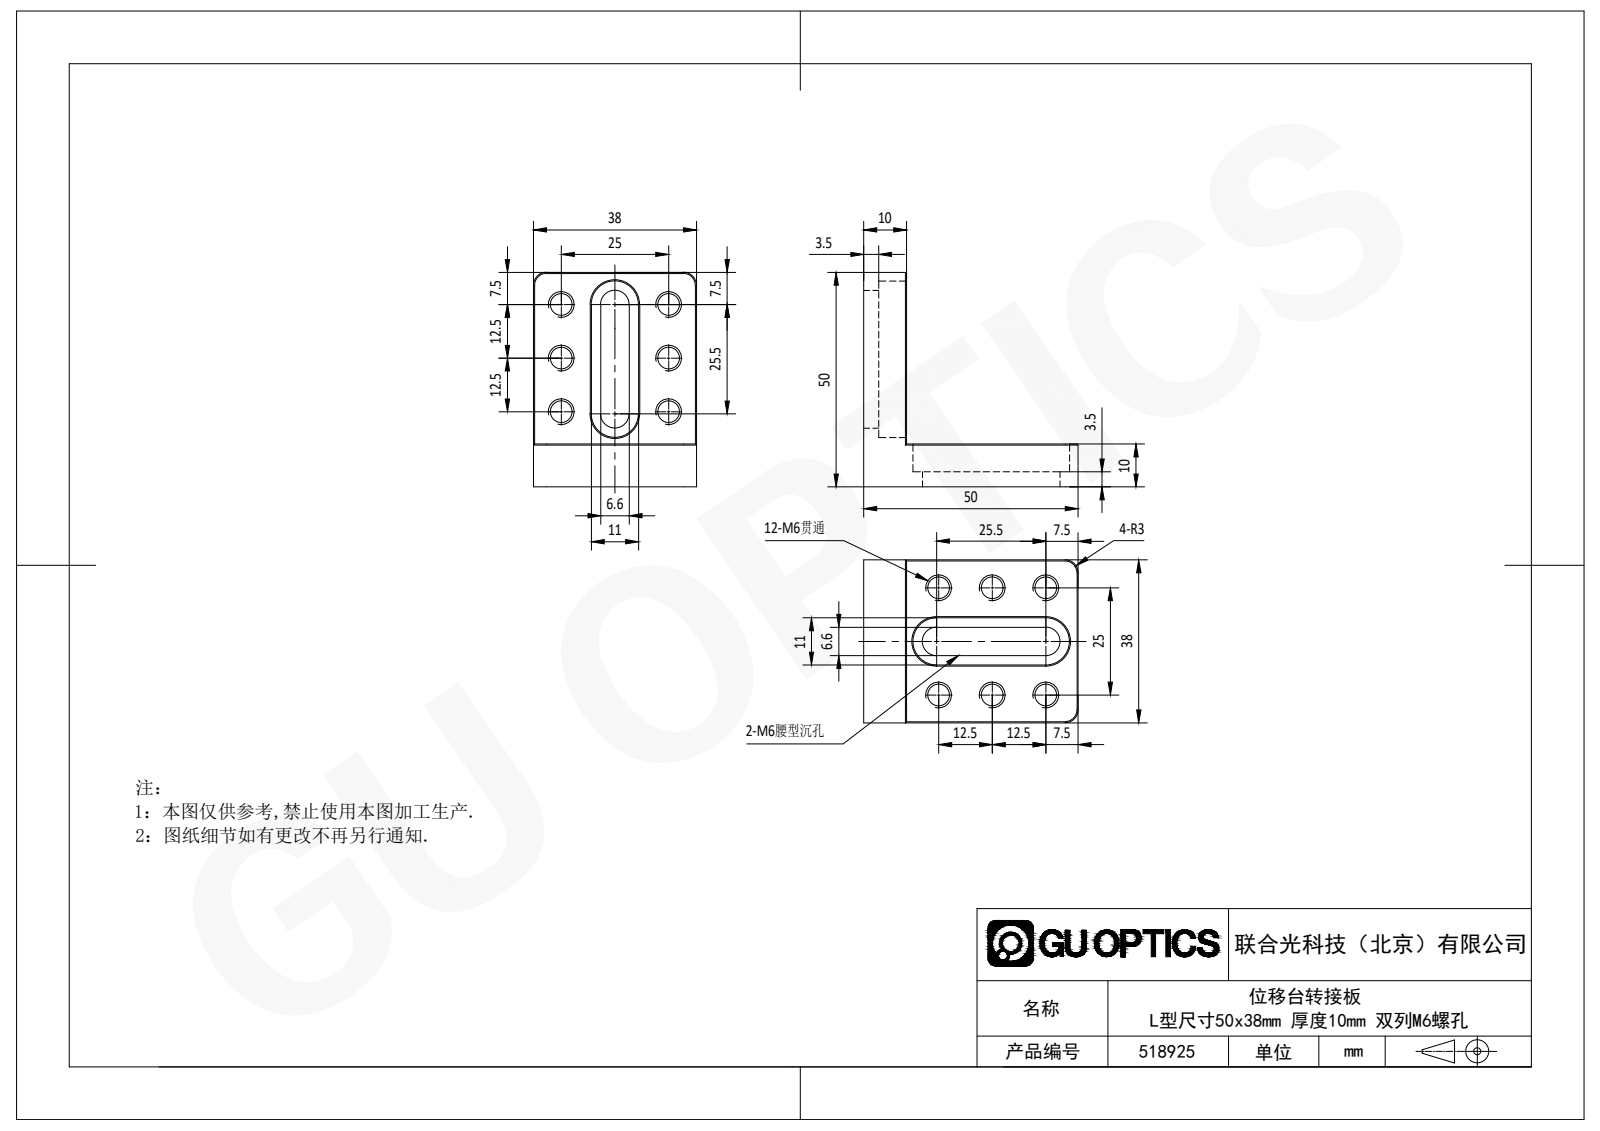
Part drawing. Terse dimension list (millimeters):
written by: SolidWorks 2020 (CONFIG_CONTROL_DESIGN)
unit: mm
bodies: 1 solid, 72 faces (28 planar, 24 cylindrical, 20 other)
size: 50 × 50 × 38
volume: 25 427 mm³; area: 11 439 mm²
holes: 12× ⌀5
rounds: 4× R3, 4× R3.3, 4× R5.5
face distances: 10, 38, 13.5, 24.5, 50, 40, 15.7, 22.3, 2.2, 8.8
hole spacings: 25, 12.5, 27.95, 35.36
